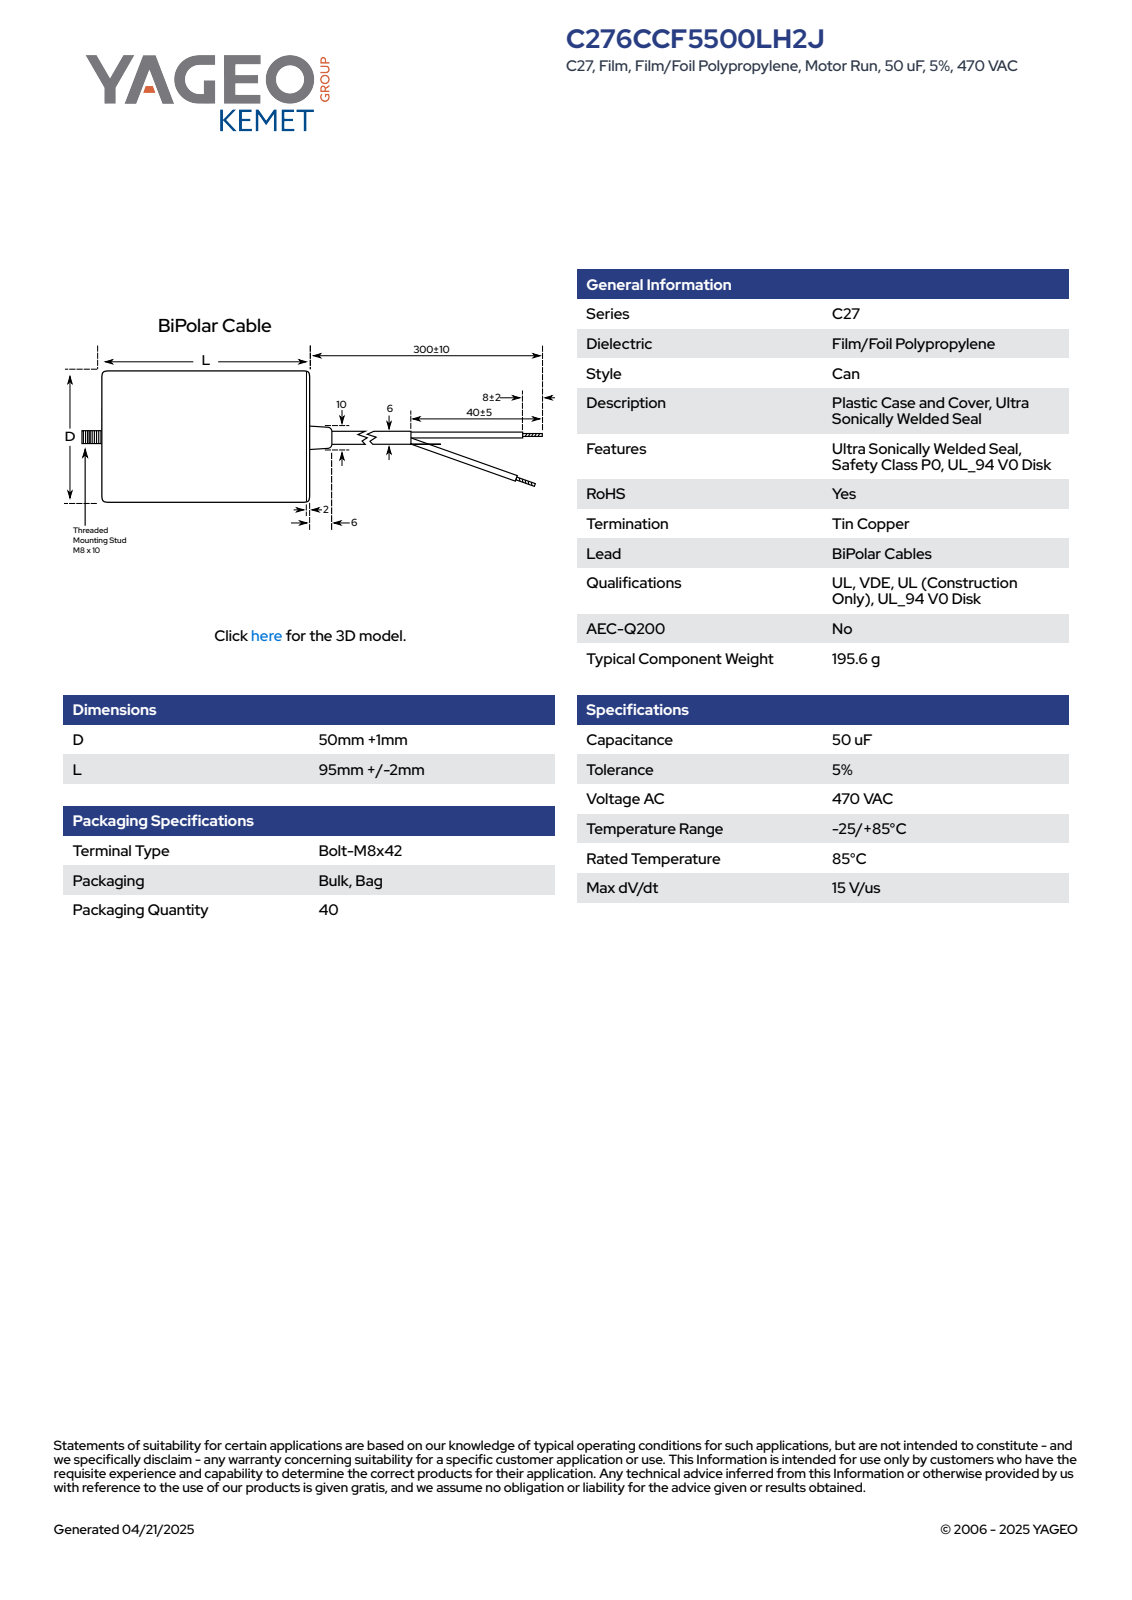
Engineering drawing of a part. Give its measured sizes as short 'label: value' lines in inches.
name: CFM_KC27BI_50X95_D51L97
written by: SolidWorks 2014 (AUTOMOTIVE_DESIGN)
unit: in
bodies: 2 solids, 82 faces (28 planar, 15 cylindrical, 39 other)
size: 4.449 × 2.008 × 2.008
volume: 11.93 in³; area: 31.51 in²
holes: 1× ⌀1.85
bosses: 1× ⌀2.008, 1× ⌀0.315
rounds: 1× R1.004
face distances: 3.74, 3.819, 0.079, 0.394, 4.134, 4.213, 4.449, 4.055, 0.315, 0.236
